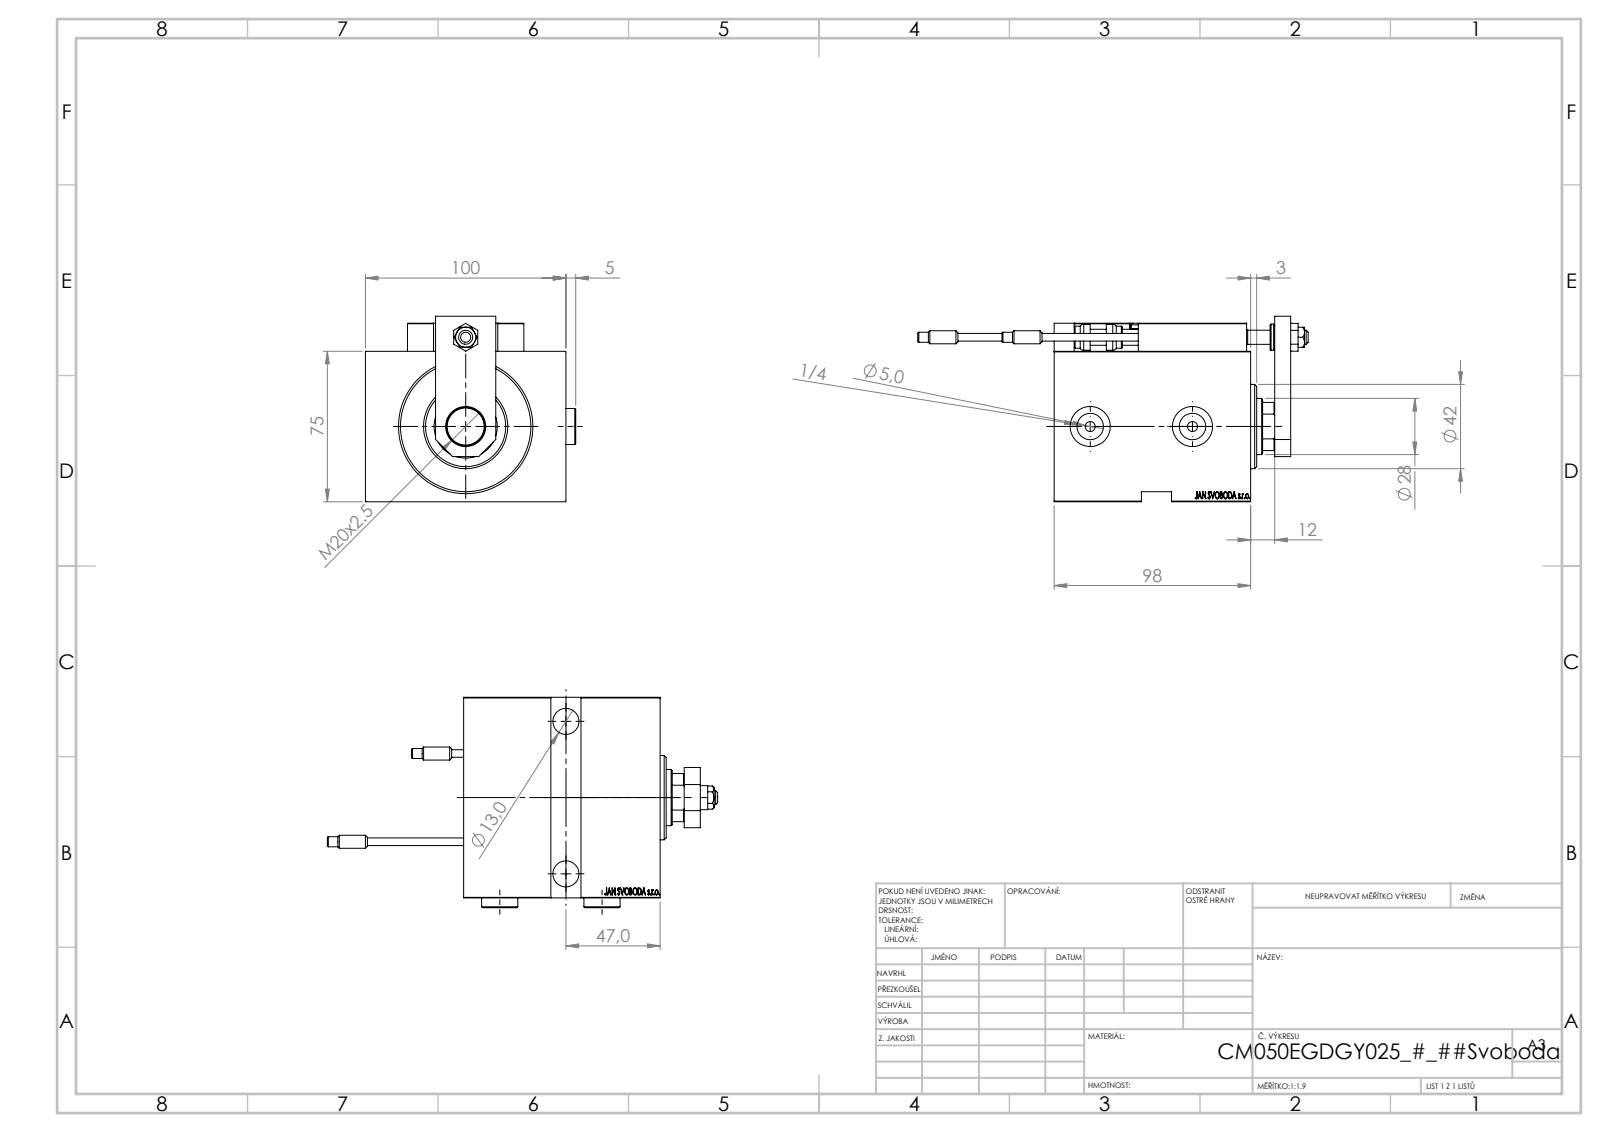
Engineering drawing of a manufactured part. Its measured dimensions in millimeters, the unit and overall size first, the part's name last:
Units: millimetres
Overall size (bounding box): 194.7 × 104.9 × 92.5
Round holes (diameter × count): ⌀8 ×5, ⌀3.2 ×4, ⌀4 ×4, ⌀5 ×4, ⌀20 ×3, ⌀13 ×2, ⌀13.16 ×2, ⌀19 ×2, ⌀7 ×1, ⌀18.5 ×1, ⌀28 ×1, ⌀31.5 ×1
Round bosses / shafts (diameter × count): ⌀5 ×4, ⌀18 ×2, ⌀6.5 ×2, ⌀3.8 ×2, ⌀52 ×1, ⌀42 ×1, ⌀13 ×1, ⌀11 ×1
Partial cylindrical surfaces — rounded edges, fillets, slot ends (radius × count): R0.3 ×30, R3 ×2, R13.5 ×1
Main face-to-face distances: 75, 14, 100, 5, 98, 84, 79, 8, 25, 32
Hole centre spacings: 11.37, 20, 29.59, 29.69, 36.06, 42.19, 48.83, 50.04
Volume: 719 283 mm³ · Surface area: 127 476 mm²
Bodies: 26 solids, 1361 faces (606 planar, 198 cylindrical, 557 other)
Part name (STEP PRODUCT): Block; NUT_D10; MAGNET; V450CM_E_VCP (+7 more)
STEP written by: SolidWorks 2019 (CONFIG_CONTROL_DESIGN)
